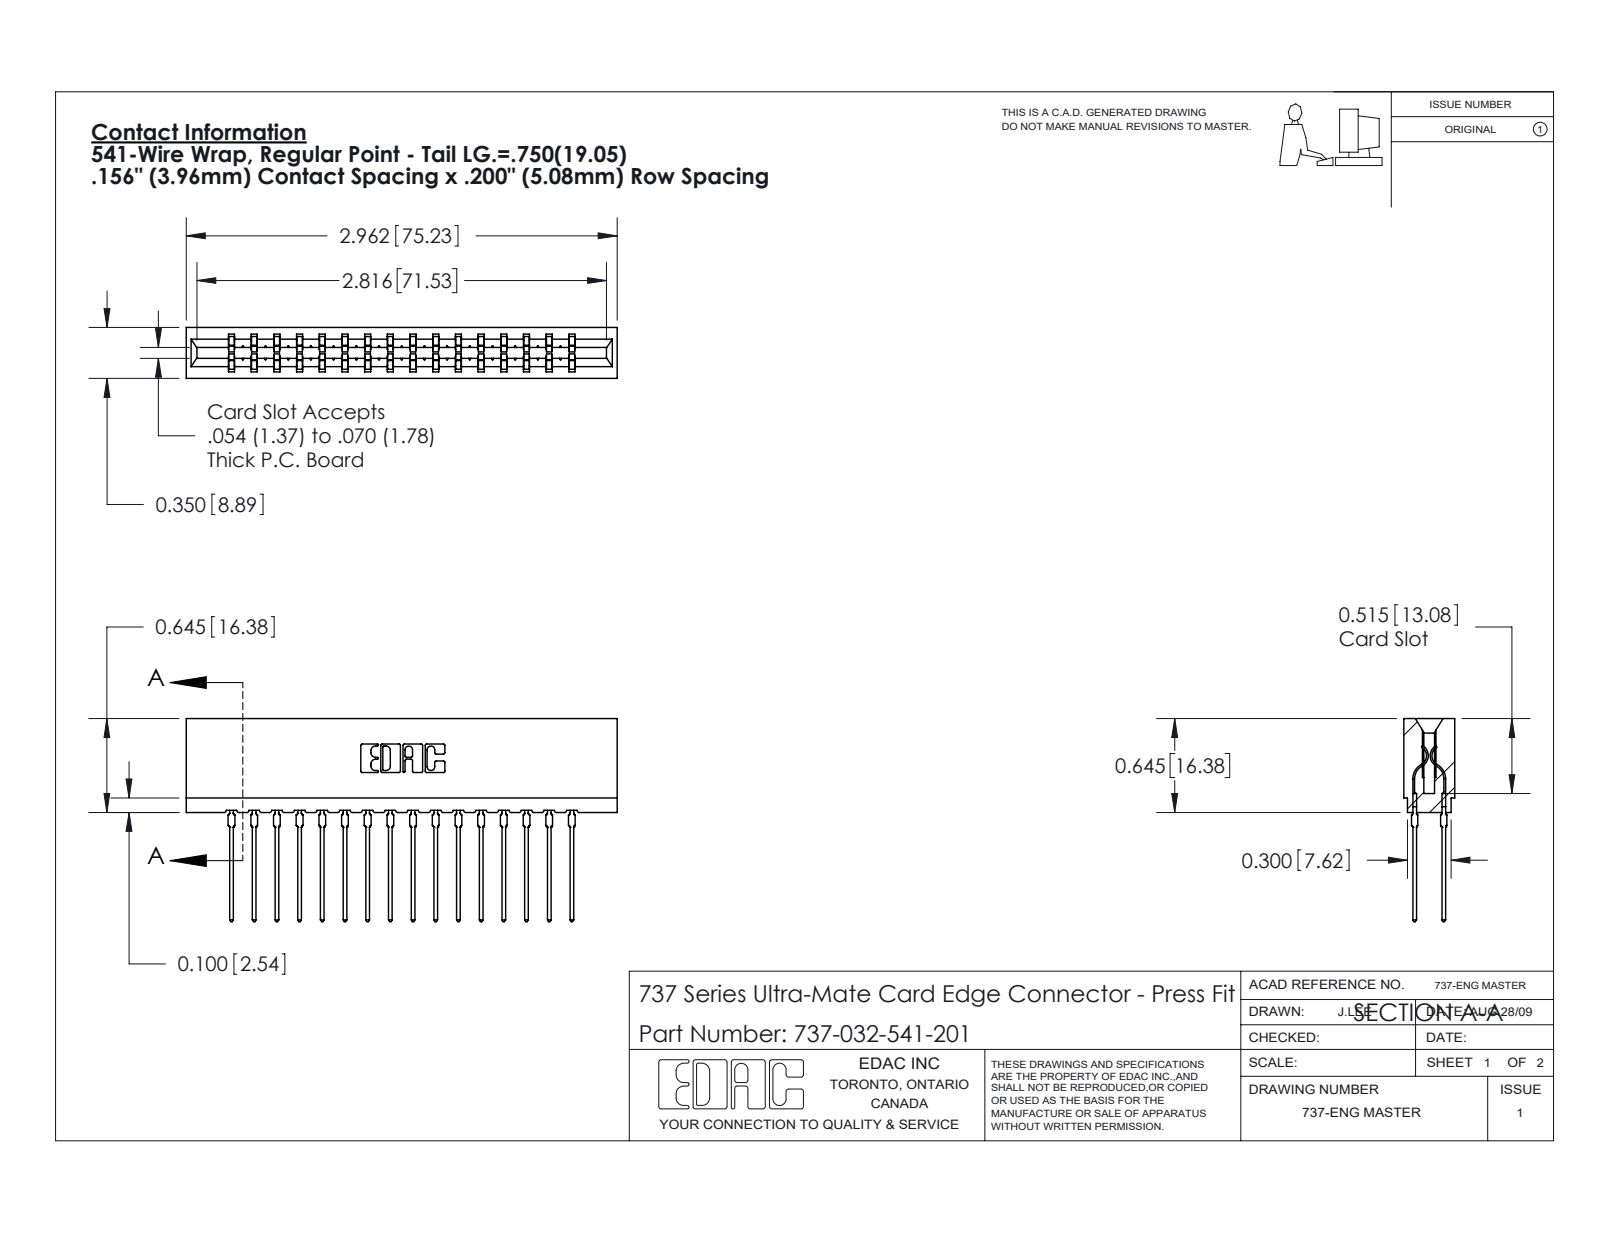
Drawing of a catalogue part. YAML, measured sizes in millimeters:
part_name: "737-032-541-201; 737 Part_Insulator Option - 01; 745-292-001_541"
step_written_by: "SolidWorks 2020 (CONFIG_CONTROL_DESIGN)"
units: millimeters
bodies: {solids: 33, faces: 2974, planar: 1542, cylindrical: 600, other: 832}
overall_size: [75.2, 35.5, 8.9]
volume: 7750
surface_area: 11420
partial_cylinders:
  - {radius: 0.5, count: 64}
  - {radius: 0.4, count: 32}
  - {radius: 0.3, count: 22}
  - {radius: 0.1, count: 8}
  - {radius: 0.3, count: 8}
  - {radius: 0.2, count: 6}
  - {radius: 0.8, count: 6}
  - {radius: 0.7, count: 3}
face_to_face_distances: [3.5, 5.4, 8.9, 4, 15.8, 1.6, 7.3, 1.9, 3.8, 19.8]
